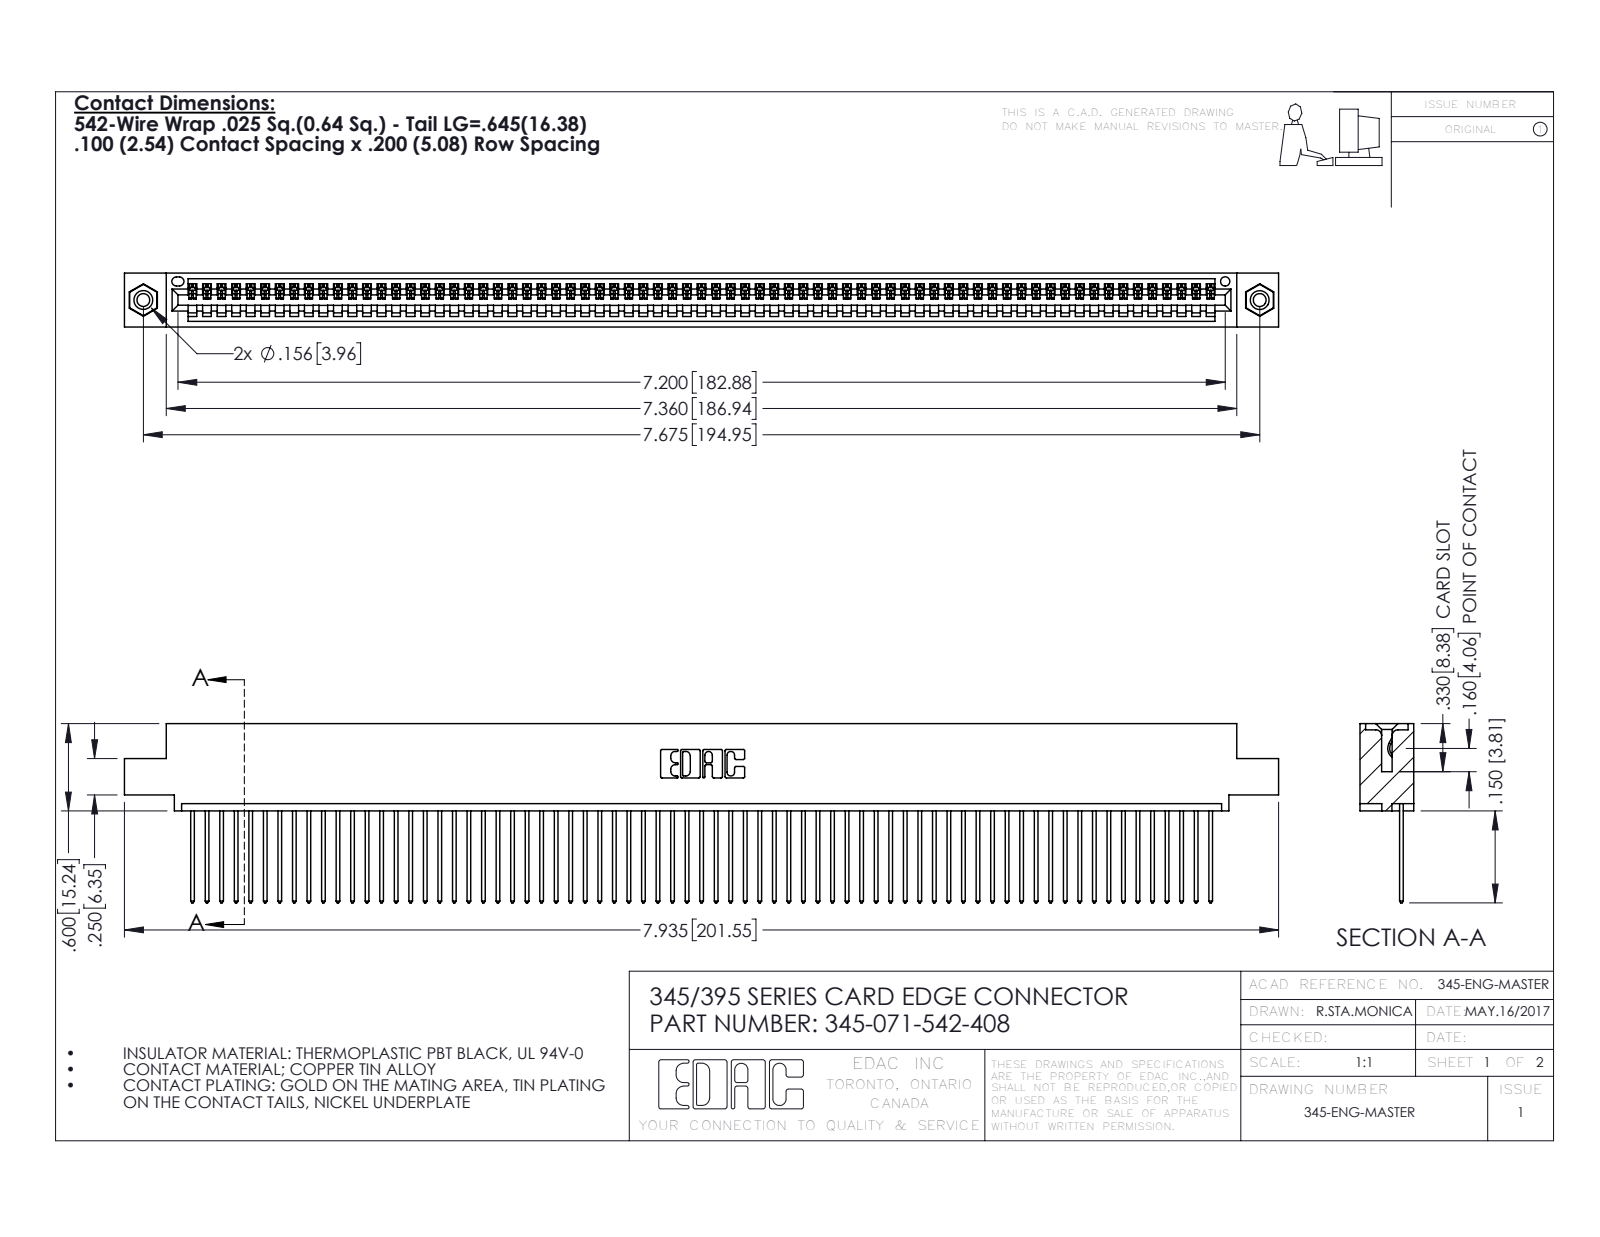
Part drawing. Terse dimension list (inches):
name: 345-292-001_345-293-142; 345 Part_0.110 Offset - 0.156 Dia-TI; 345-071-542-408; 345-250-001_345-250-003-102
written by: SolidWorks 2016 (CONFIG_CONTROL_DESIGN)
unit: in
bodies: 74 solids, 4308 faces (2956 planar, 1336 cylindrical, 16 other)
size: 7.935 × 1.232 × 0.37
volume: 1.187 in³; area: 42.4 in²
holes: 2× ⌀0.089, 2× ⌀0.125, 2× ⌀0.156, 1× ⌀0.064
bosses: 2× ⌀0.155
rounds: 142× R0.006, 142× R0.01, 22× R0.01, 6× R0.007, 6× R0.031, 3× R0.026, 2× R0.031, 2× R0.04
face distances: 0.072, 0.298, 0.098, 0.272, 0.025, 0.37, 0.2, 0.225, 0.149, 0.072
hole spacings: 0.27, 7.439, 7.675
